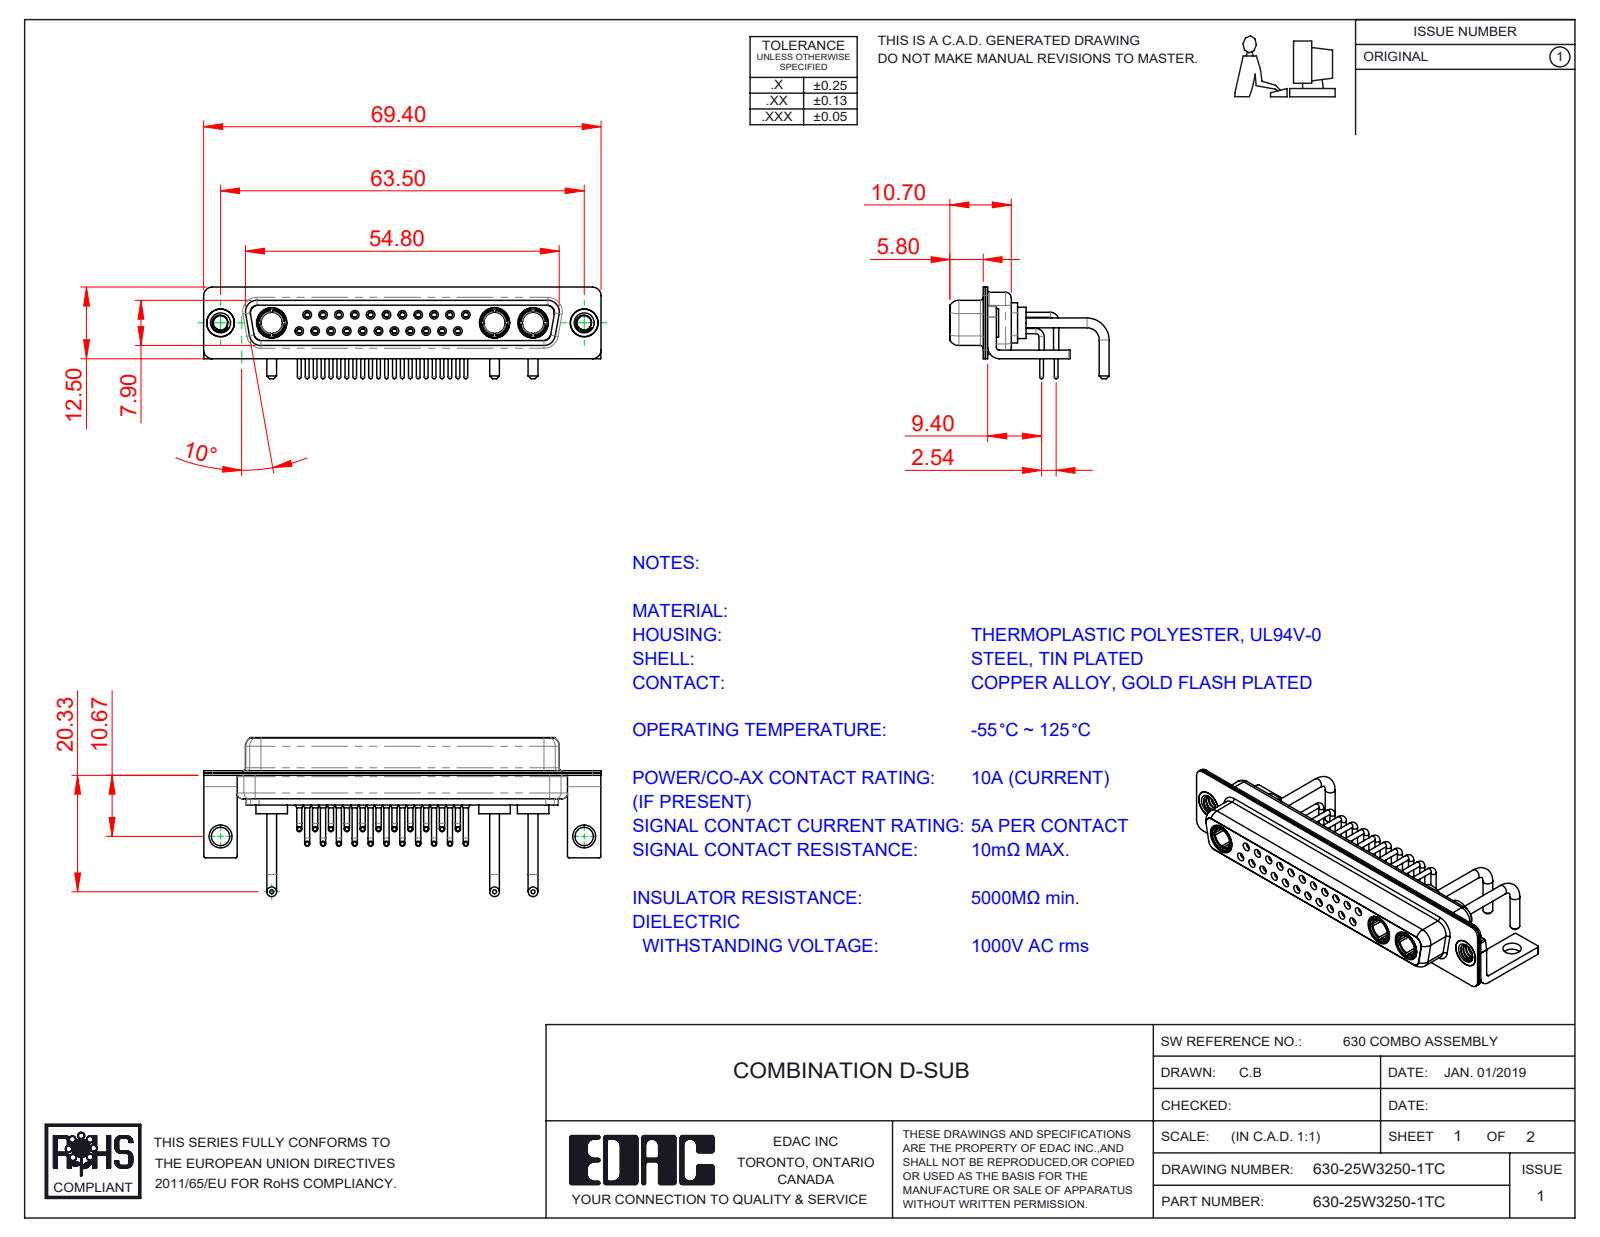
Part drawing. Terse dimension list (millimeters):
name: 630Combo Housing_25W3; 630Combo Shell Rear_37 Contacts; 630Combo Shell Front_37 Contacts; 630Combo Contact Row 2 (+5 more)
written by: SolidWorks 2020 (CONFIG_CONTROL_DESIGN)
unit: mm
bodies: 35 solids, 1717 faces (504 planar, 736 cylindrical, 477 other)
size: 69.4 × 27.78 × 16
volume: 5 813 mm³; area: 13 265 mm²
holes: 22× ⌀0.9, 22× ⌀1.1, 22× ⌀1.5, 22× ⌀2, 11× ⌀1.6, 11× ⌀1.7, 5× ⌀4.85, 3× ⌀3.7, 3× ⌀5.3, 2× ⌀2.5, 2× ⌀3.2, 2× ⌀4
bosses: 23× ⌀0.9, 22× ⌀0.65, 12× ⌀1.6, 6× ⌀1.7, 3× ⌀5.5, 3× ⌀5.2, 3× ⌀4.96, 3× ⌀4.75
rounds: 16× R0.25, 16× R1.5, 13× R2, 8× R1.35, 8× R1.6, 5× R0.5, 4× R0.6, 4× R0.65
face distances: 0.4, 0.45, 1.4, 8.45, 1.8, 8.9, 6.2, 7.05, 0.8, 7.5
hole spacings: 3.16, 2.77, 5.54, 5.03, 8.31, 7.48, 11.08, 5.04
